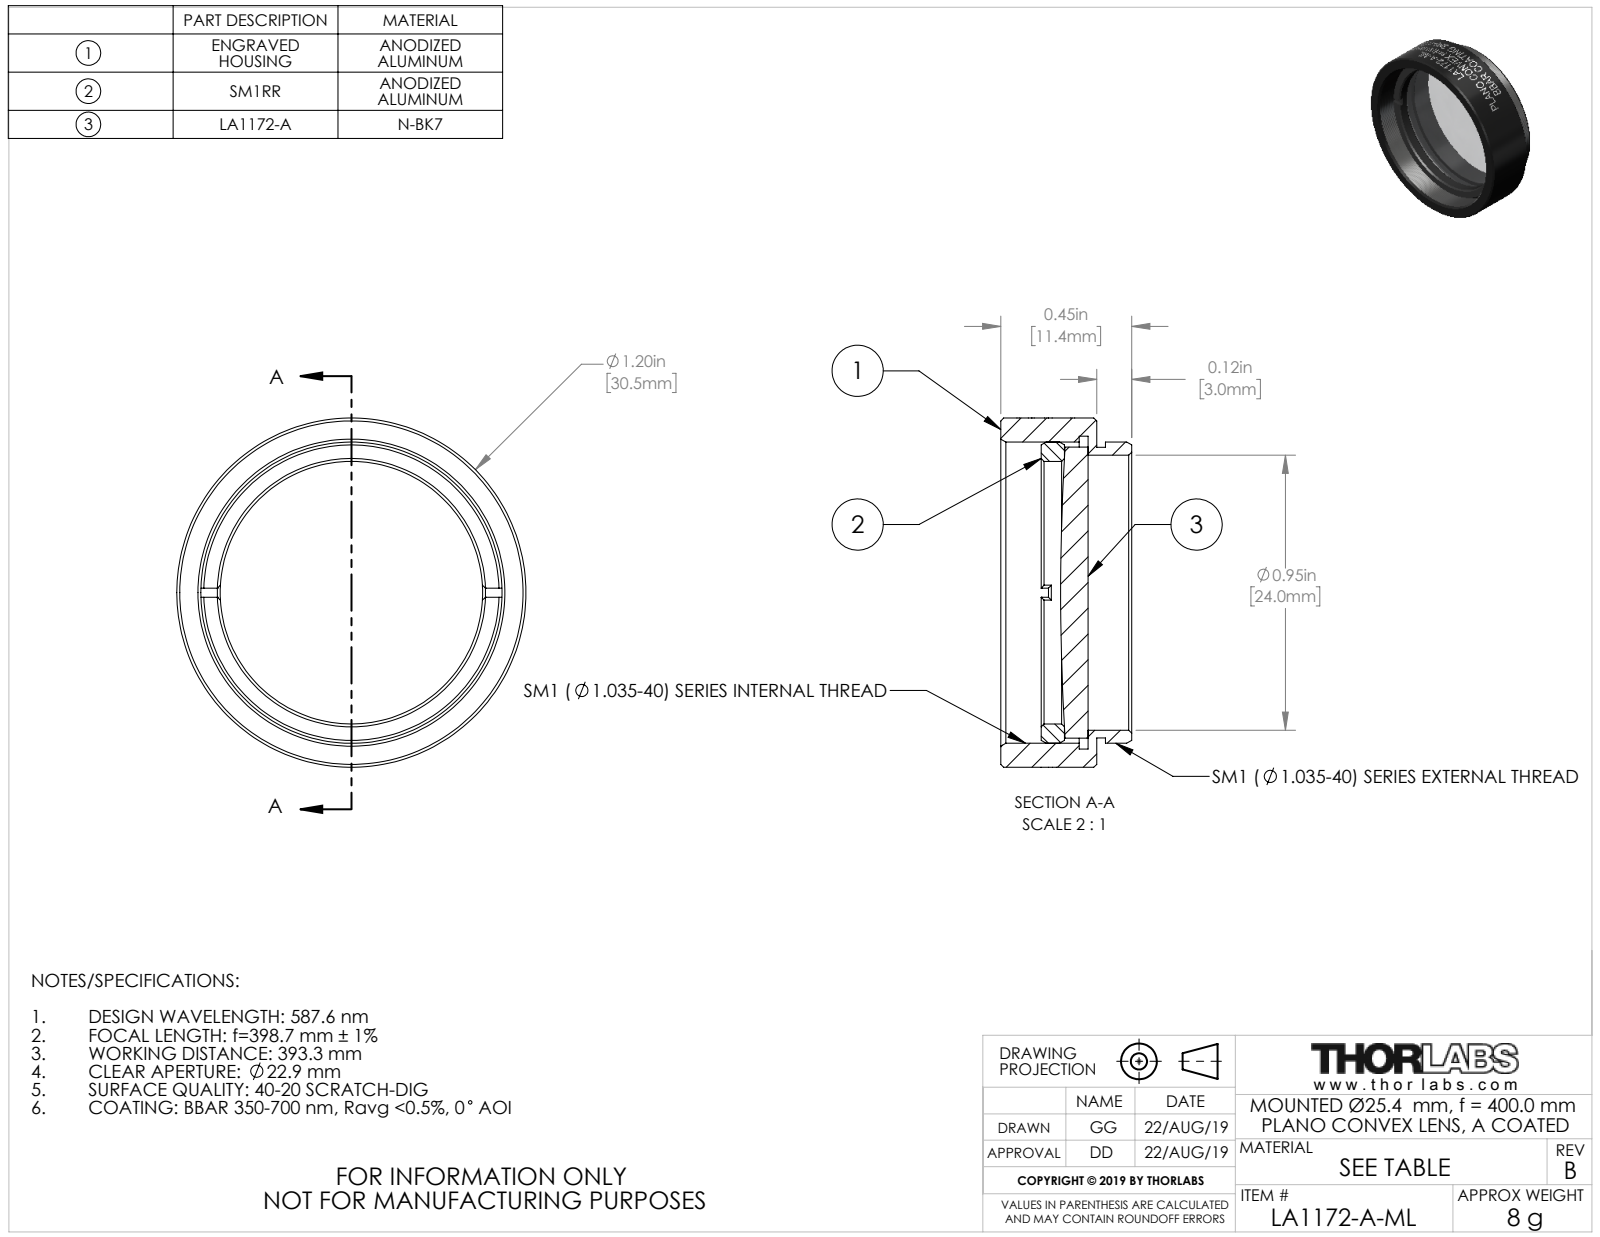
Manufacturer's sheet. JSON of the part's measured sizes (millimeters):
{"part_name": "24447-E0W", "step_written_by": "SolidWorks 2018 (CONFIG_CONTROL_DESIGN)", "units": "millimeters", "bodies": {"solids": 3, "faces": 152, "planar": 20, "cylindrical": 108, "other": 24}, "overall_size": [30.48, 30.48, 11.43], "volume_mm3": 3193, "surface_area_mm2": 4313, "round_holes": [[22.91, 1], [24, 1], [27.3, 1]], "round_bosses_or_shafts": [[30.48, 1], [26.29, 1], [25.4, 1], [25.37, 1]], "face_to_face_distances": [0.76, 8.38, 7.62, 2.82, 2.06, 5.56, 4.85, 4.09, 2.03, 3.53]}
